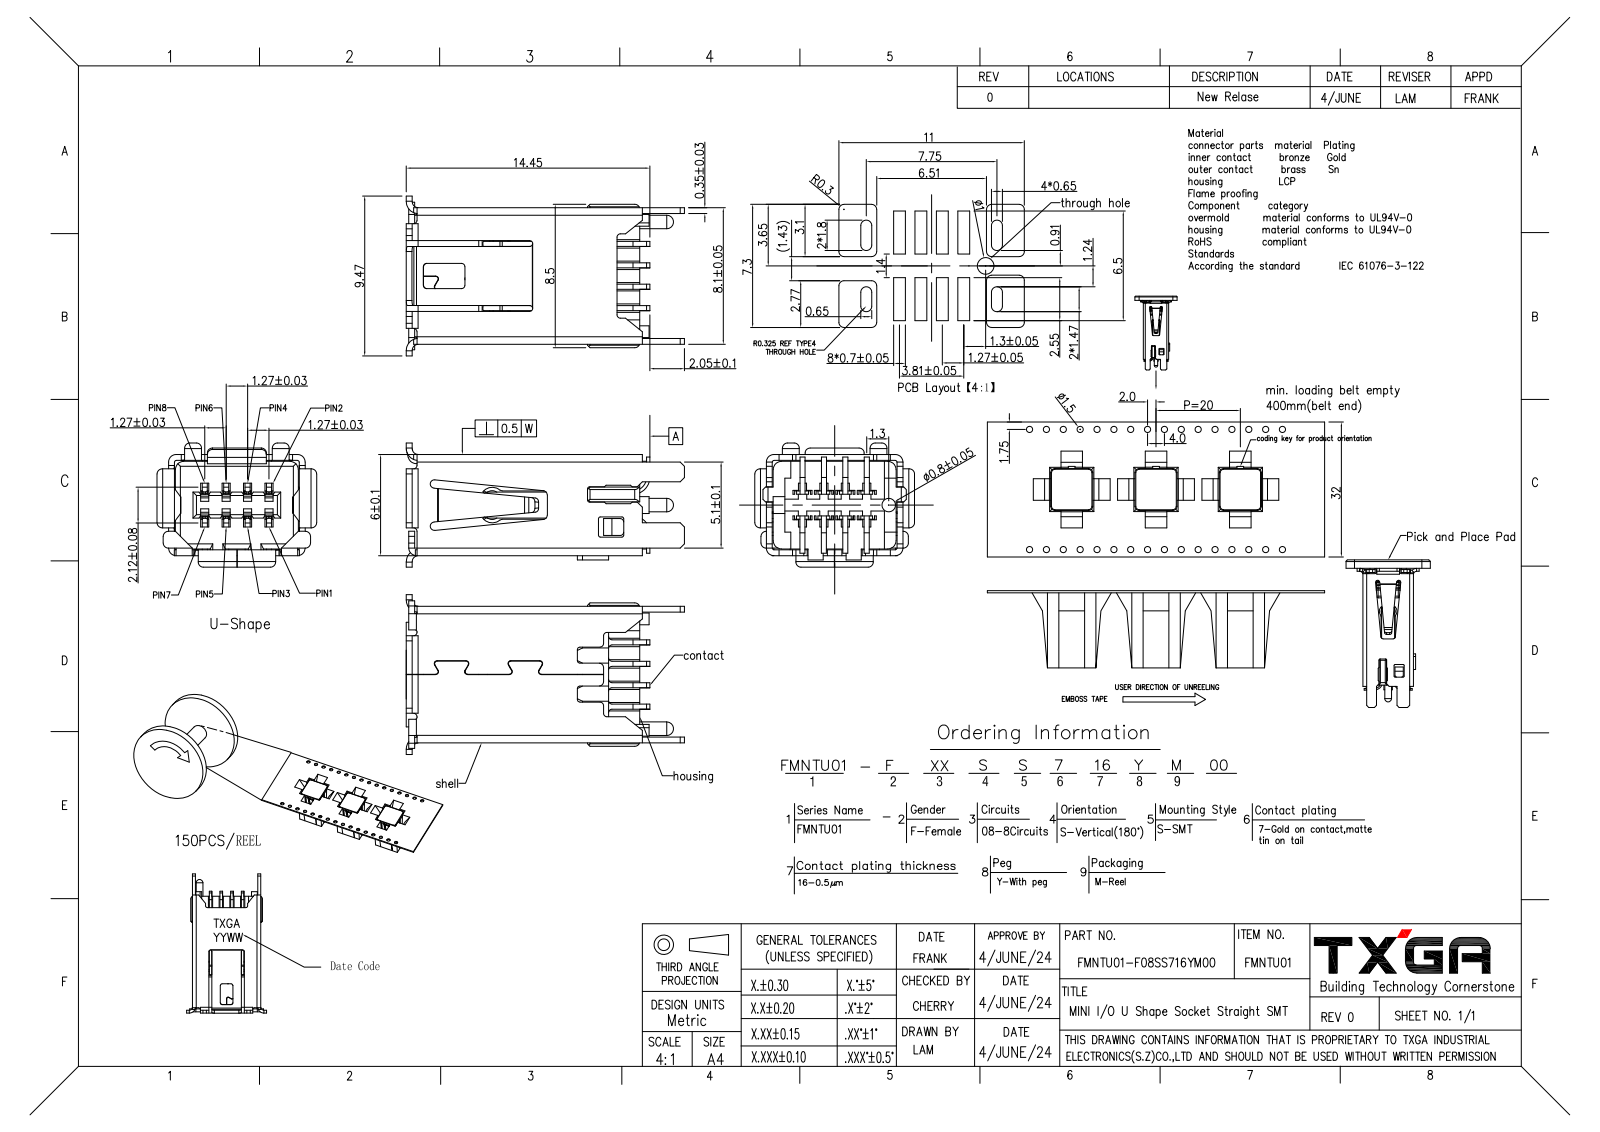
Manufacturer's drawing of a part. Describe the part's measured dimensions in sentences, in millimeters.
The part is named "FMINI-SUST1XX-000". Its 3-D file was written by "PRO/ENGINEER BY PARAMETRIC TECHNOLOGY CORPORATION, 2010280 (CONFIG_CONTROL_DESIGN)". It is 1 solid with 1114 faces: 790 planar, 322 cylindrical and 2 other. Overall it measures 16.5 by 9.47 by 7.36 millimeters. Its volume is 259 cubic millimeters and its surface area 1 133 square millimeters. Round bosses or shafts: 1 of diameter 0.8. Partial cylindrical surfaces (rounded edges, fillets, slot ends): 38 of radius 0.1, 38 of radius 0.15, 32 of radius 0.2, 18 of radius 0.3, 10 of radius 0.25, 10 of radius 0.7, 8 of radius 0.17, 8 of radius 0.35. The main face-to-face distances are 0.35, 5.65, 7.75, 6, 5.3, 7.4, 0.4, 8.1, 1.1, 6.65.
